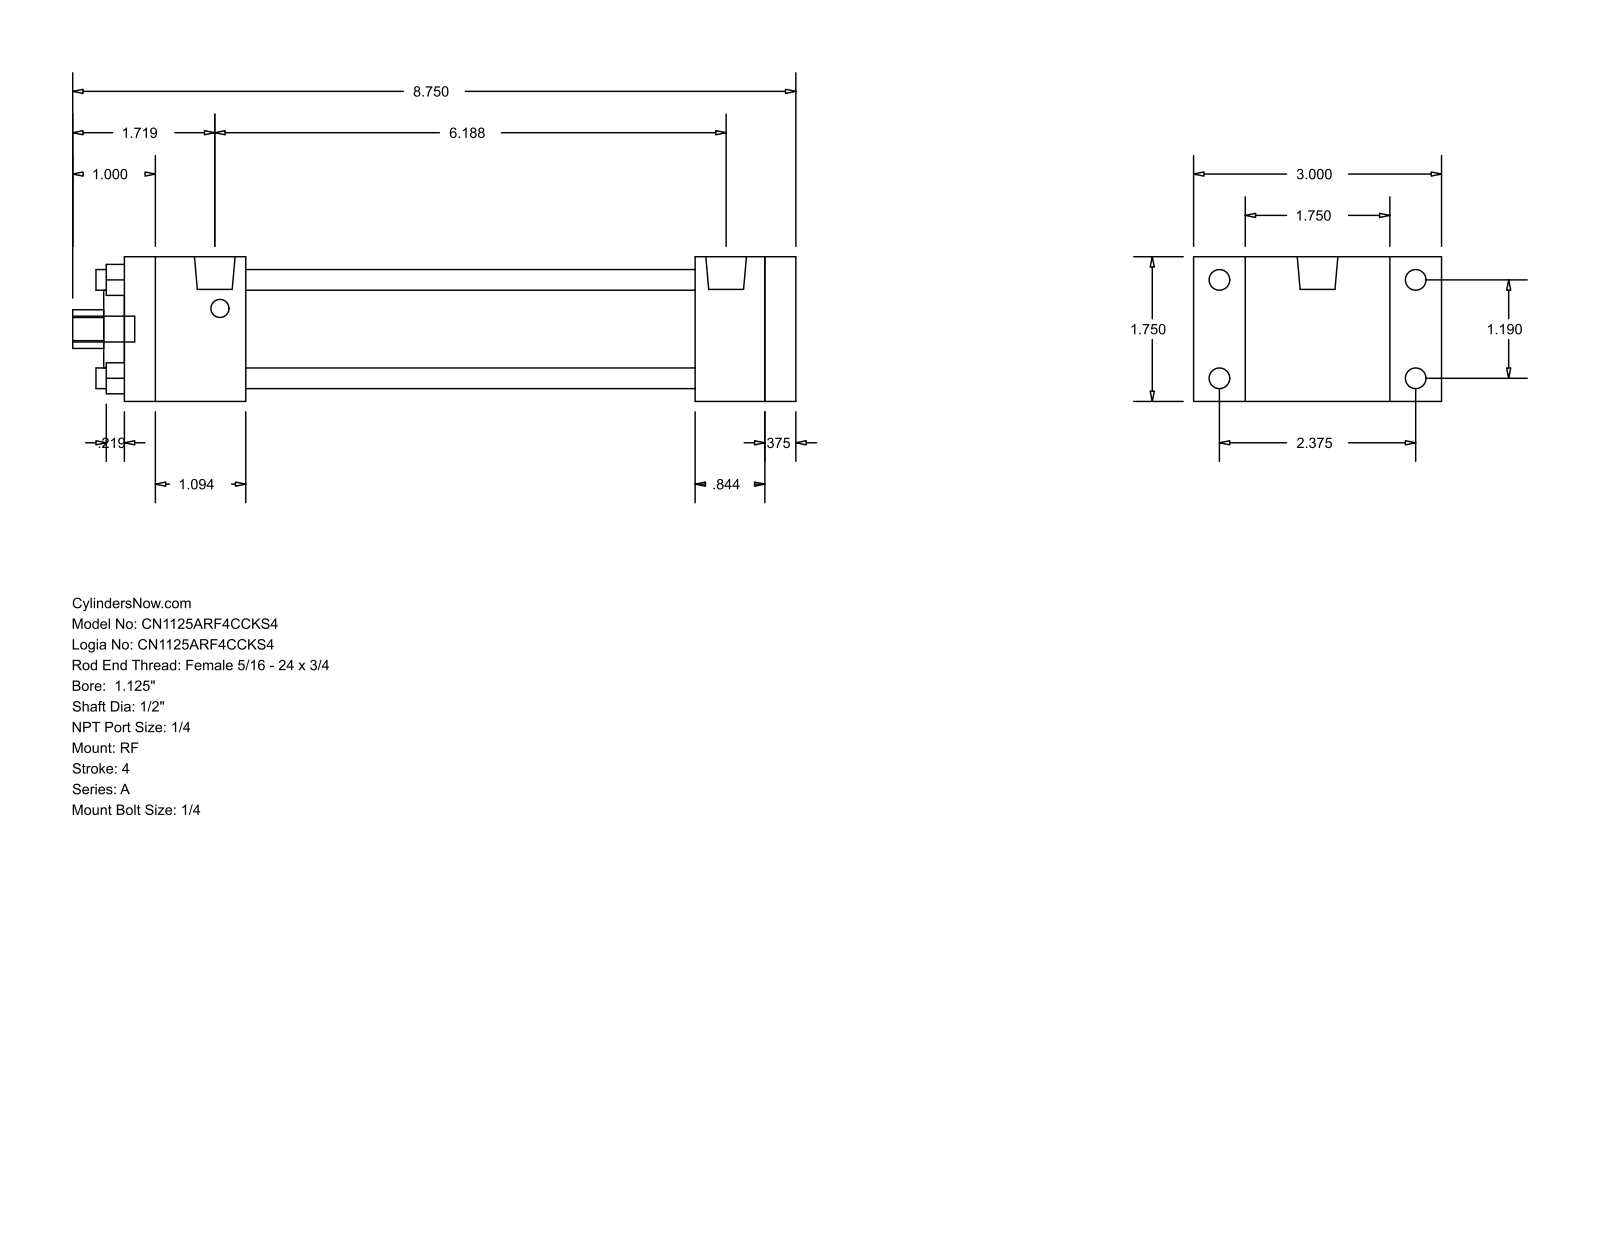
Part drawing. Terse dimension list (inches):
name: A_RF__0112_0.5
written by: GSSL Pune (CONFIG_CONTROL_DESIGN)
unit: in
bodies: 0 solids, 92 faces (64 planar, 28 cylindrical, 0 other)
size: 8.75 × 3 × 1.75
holes: 4× ⌀0.25, 1× ⌀0.5, 1× ⌀0.937, 1× ⌀1.255
bosses: 4× ⌀0.25, 4× ⌀0.219, 2× ⌀0.492, 1× ⌀0.313
rounds: 1× R0.234
face distances: 1.75, 0.375, 8.125, 7.75, 1.469, 6.906, 5.437, 6.281, 6.656, 0.844
hole spacings: 0.841, 1.19, 1.683
